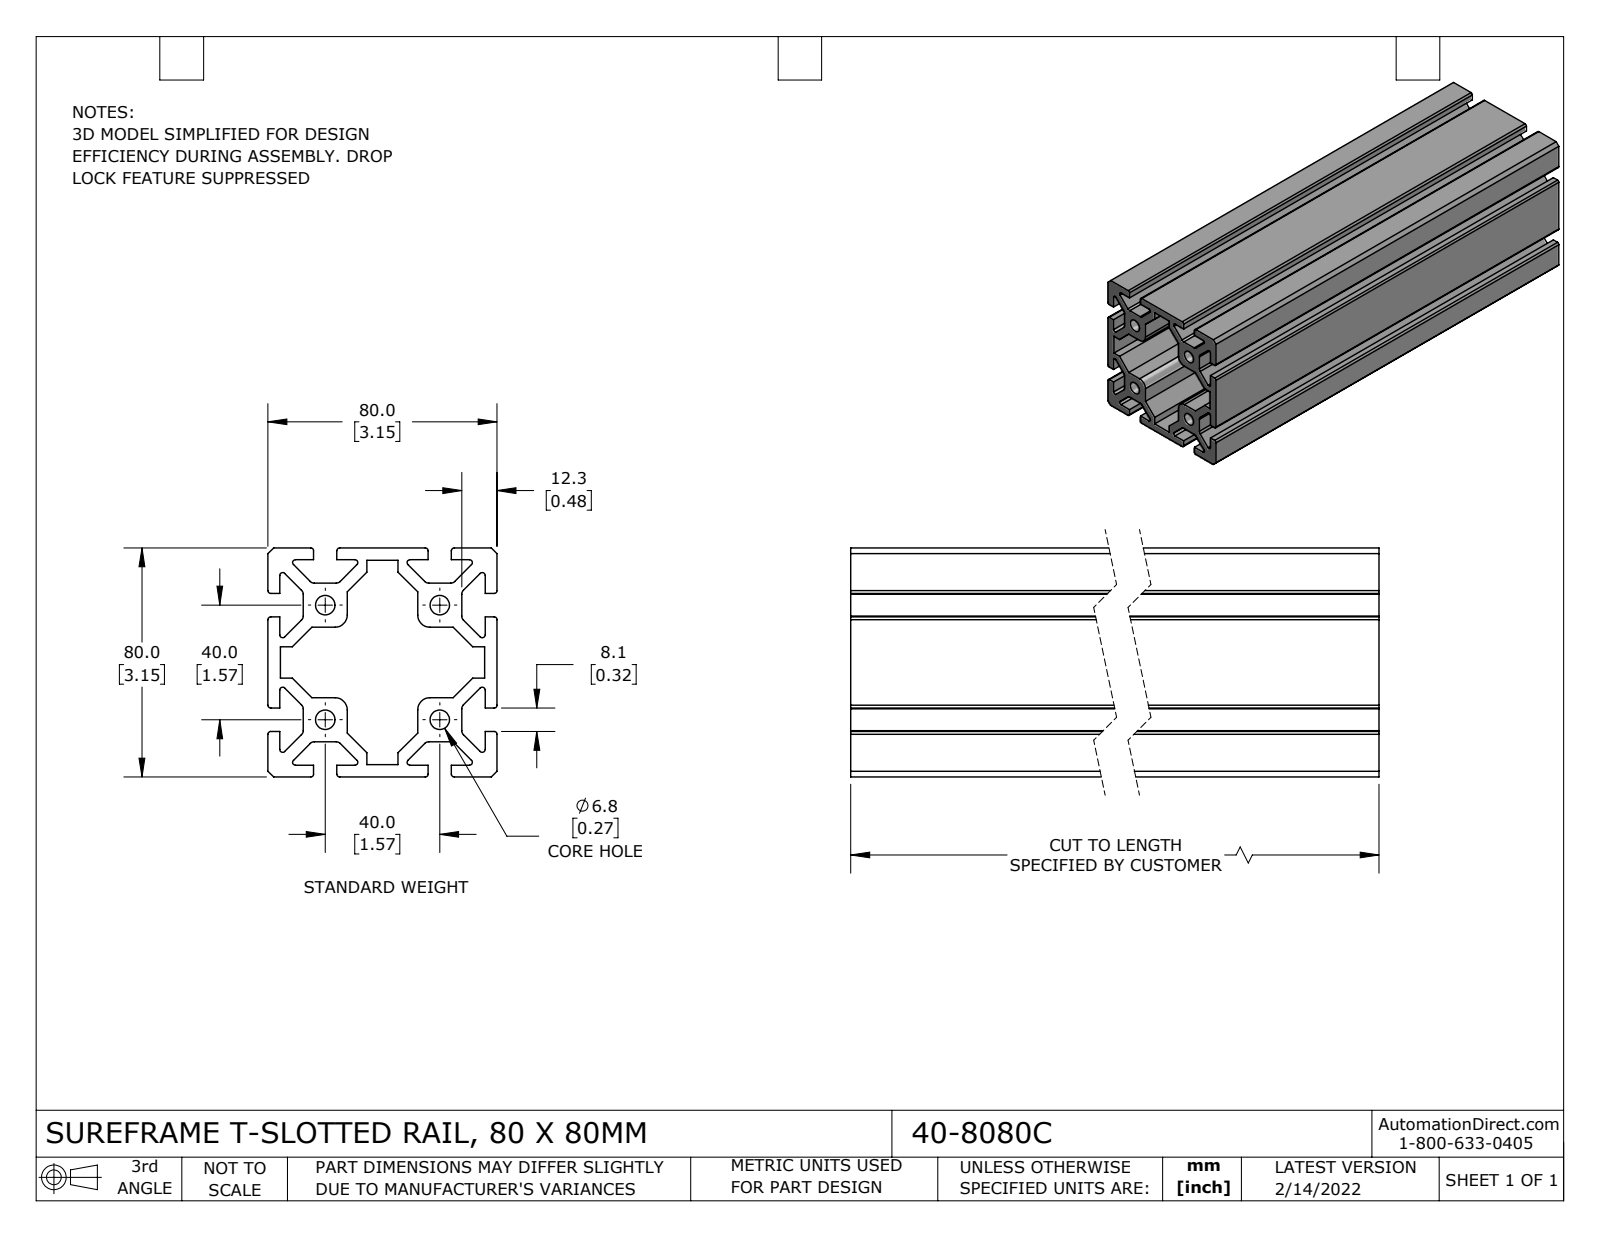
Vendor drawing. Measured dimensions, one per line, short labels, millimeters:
name: 40-8080C
written by: SolidWorks 2021 (CONFIG_CONTROL_DESIGN)
unit: mm
bodies: 1 solid, 170 faces (102 planar, 68 cylindrical, 0 other)
size: 254 × 80 × 80
volume: 597 126 mm³; area: 258 477 mm²
holes: 4× ⌀6.81
rounds: 32× R1, 16× R2, 4× R4.25
face distances: 4.32, 28.28, 80, 4.14, 75.86, 40, 23.96, 32.6, 56.56, 27.7
hole spacings: 40, 56.57
